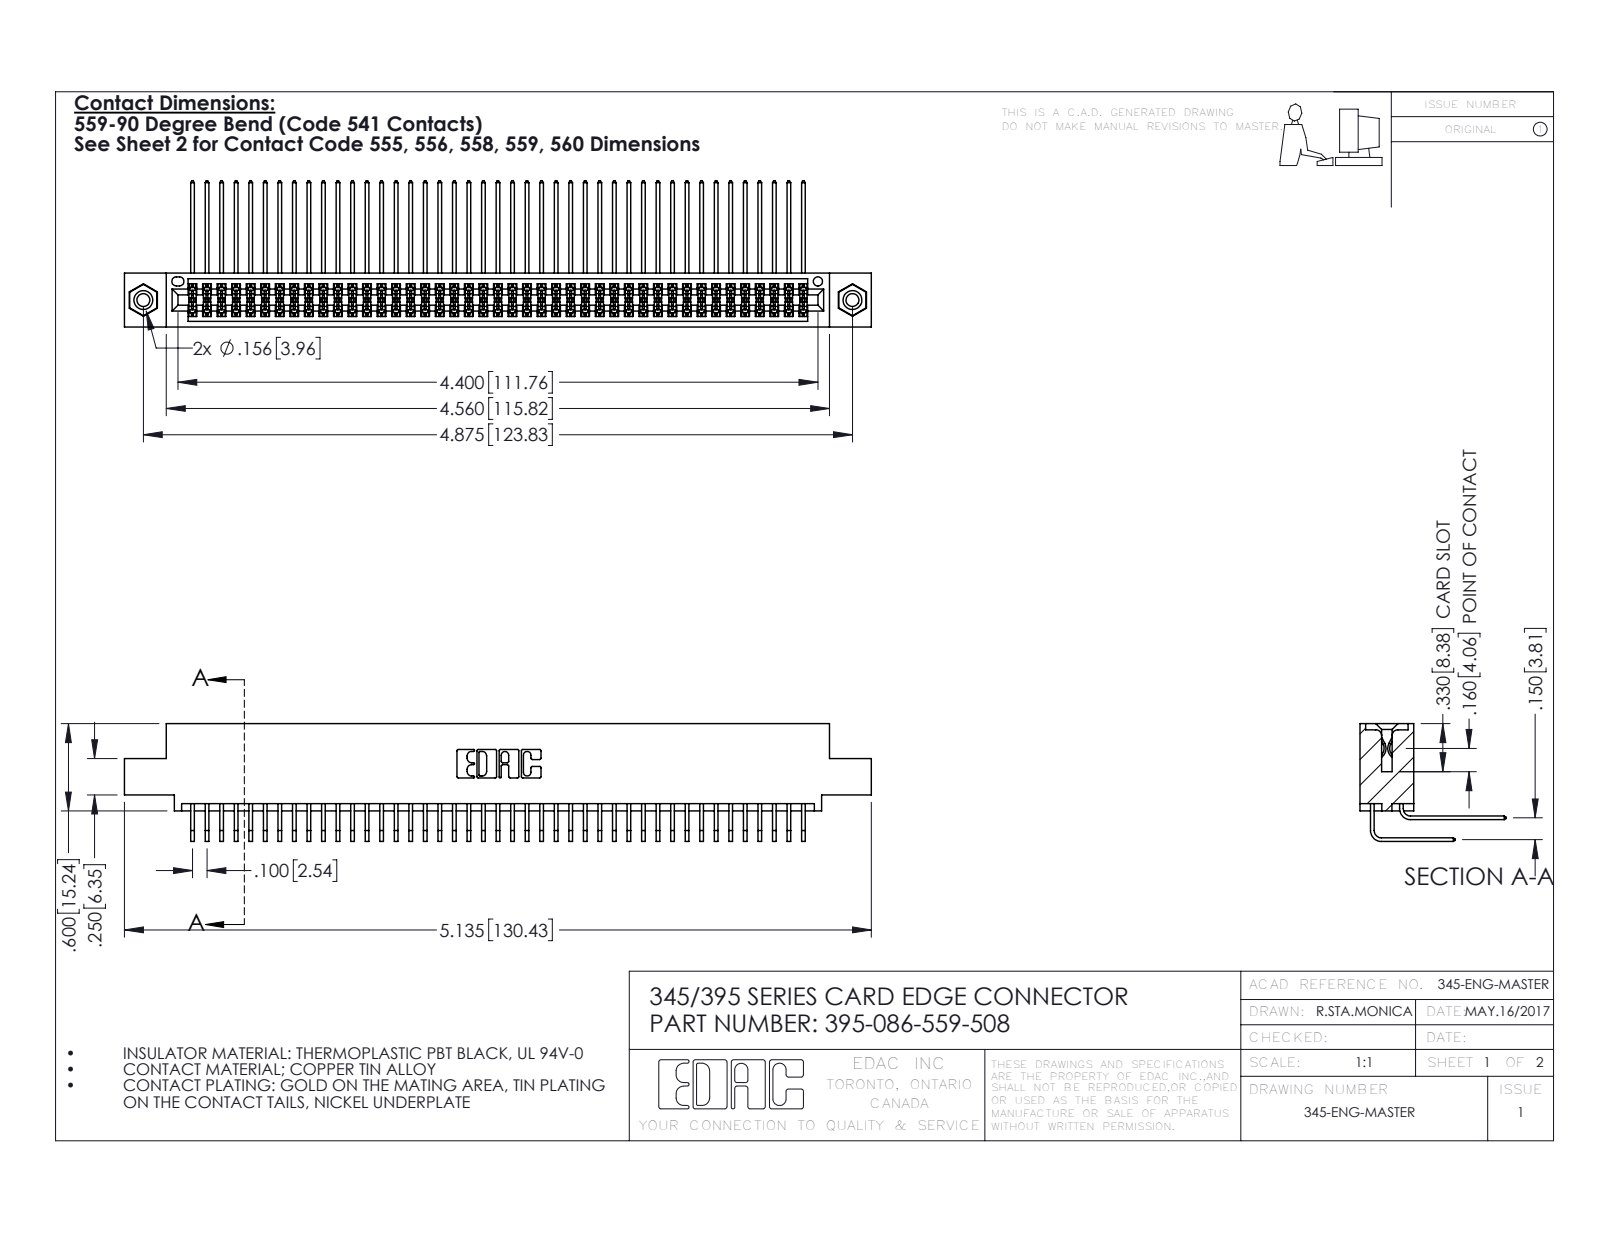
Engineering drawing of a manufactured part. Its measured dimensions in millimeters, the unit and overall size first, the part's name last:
Units: millimetres
Overall size (bounding box): 130.4 × 25.5 × 20.5
Round holes (diameter × count): ⌀2.3 ×2, ⌀3.2 ×2, ⌀4 ×2, ⌀1.6 ×1
Round bosses / shafts (diameter × count): ⌀3.9 ×2
Partial cylindrical surfaces — rounded edges, fillets, slot ends (radius × count): R0.2 ×130, R0.3 ×22, R0.2 ×6, R0.8 ×6, R0.7 ×3, R0.4 ×2, R0.5 ×2, R0.6 ×2
Main face-to-face distances: 1.8, 7.6, 5.1, 9.4, 2.5, 6.9, 0.6, 5.7, 4.4, 3.8
Hole centre spacings: 6.9, 117.8, 123.8
Volume: 13 100 mm³ · Surface area: 21 810 mm²
Bodies: 89 solids, 4662 faces (3126 planar, 1520 cylindrical, 16 other)
Part name (STEP PRODUCT): 345 Part_0.110 Offset - 0.156 Dia-TI; 345-292-001_558 559 Tail - 1; 345-292-001_559 Tail - 2; 395-086-559-508 (+1 more)
STEP written by: SolidWorks 2016 (CONFIG_CONTROL_DESIGN)
